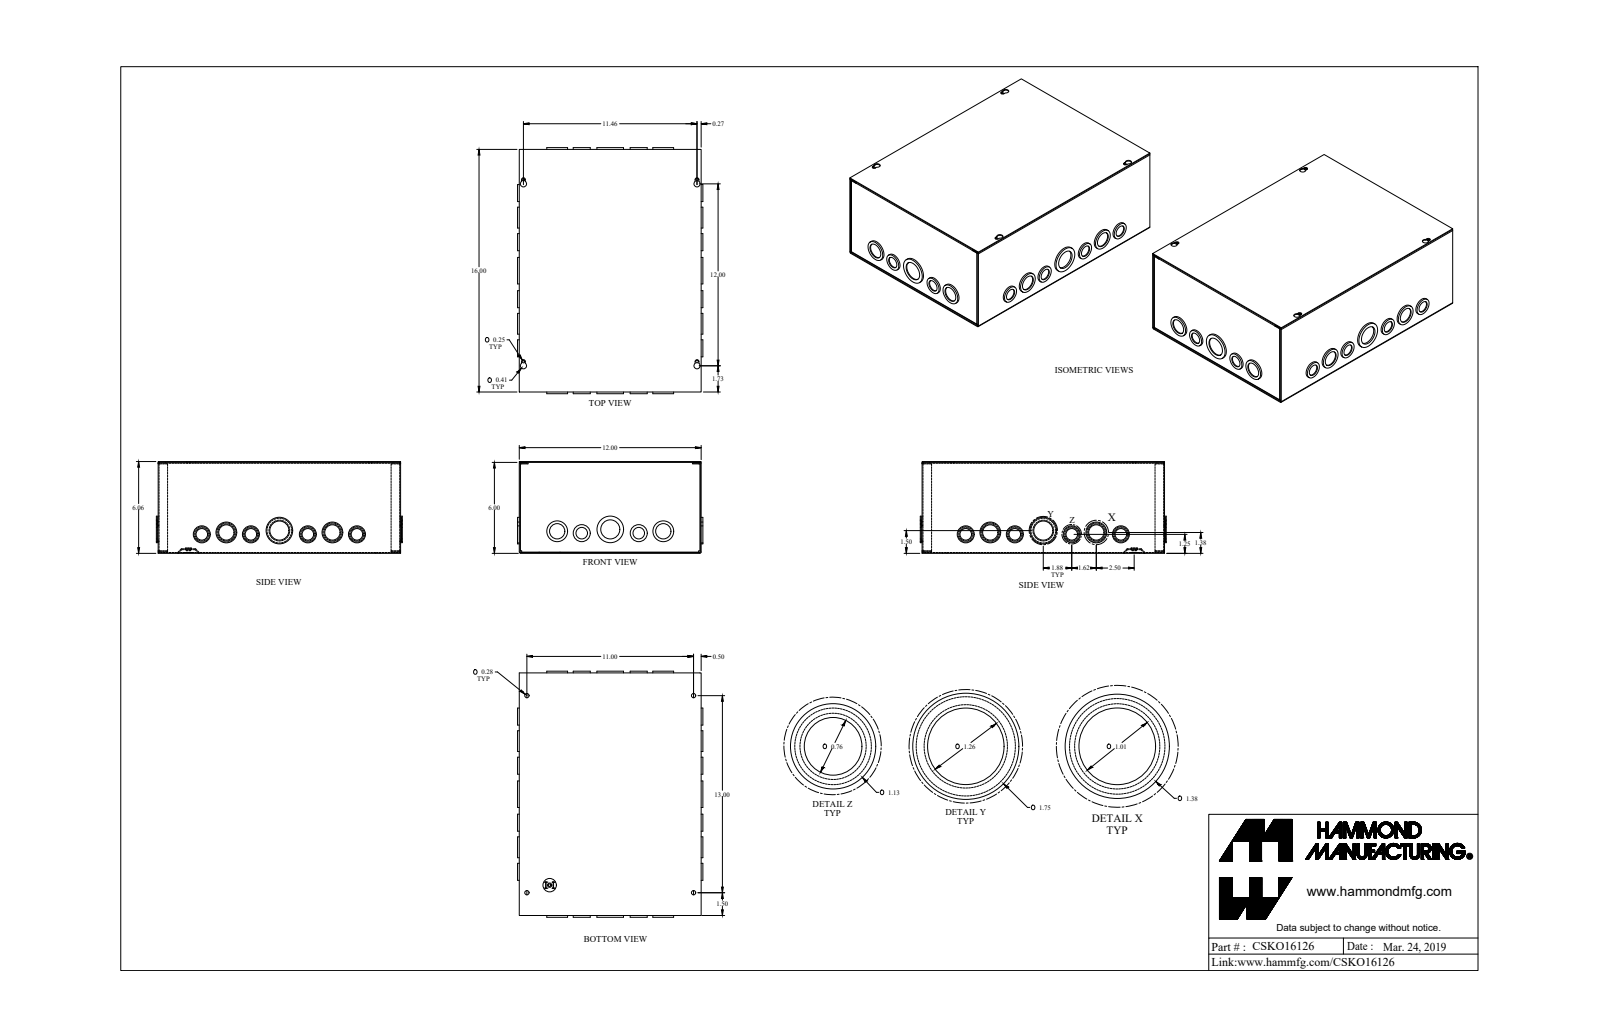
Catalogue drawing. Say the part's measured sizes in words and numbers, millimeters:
The part is named "CSKO16126_Default". Its 3-D file was written by "SolidWorks 2019 (CONFIG_CONTROL_DESIGN)". It is 4 solids with 493 faces: 221 planar, 264 cylindrical and 8 other. Overall it measures 412.3 by 310.7 by 153.8 millimeters. Its volume is 725 500 cubic millimeters and its surface area 1 010 000 square millimeters. Round holes: 10 of diameter 25.7, 6 of diameter 19.3, 6 of diameter 32, 5 of diameter 4.3, 4 of diameter 7.1, 2 of diameter 41.6, 1 of diameter 12.7. Round bosses or shafts: 8 of diameter 28.6, 6 of diameter 22.2, 6 of diameter 22.2, 5 of diameter 34.9, 3 of diameter 34.9, 2 of diameter 44.5, 2 of diameter 28.6, 1 of diameter 12.5. Partial cylindrical surfaces (rounded edges, fillets, slot ends): 12 of radius 0.7, 12 of radius 2.2, 8 of radius 1.4, 4 of radius 3.2, 4 of radius 5.2. The main face-to-face distances are 1.4, 152.4, 151, 153.8, 303.4, 405, 304.8, 301.9, 406.4, 403.5. The hole center spacings are 41.3, 14, 48.2, 89, 136.7, 177.8, 285.5, 317.6.
